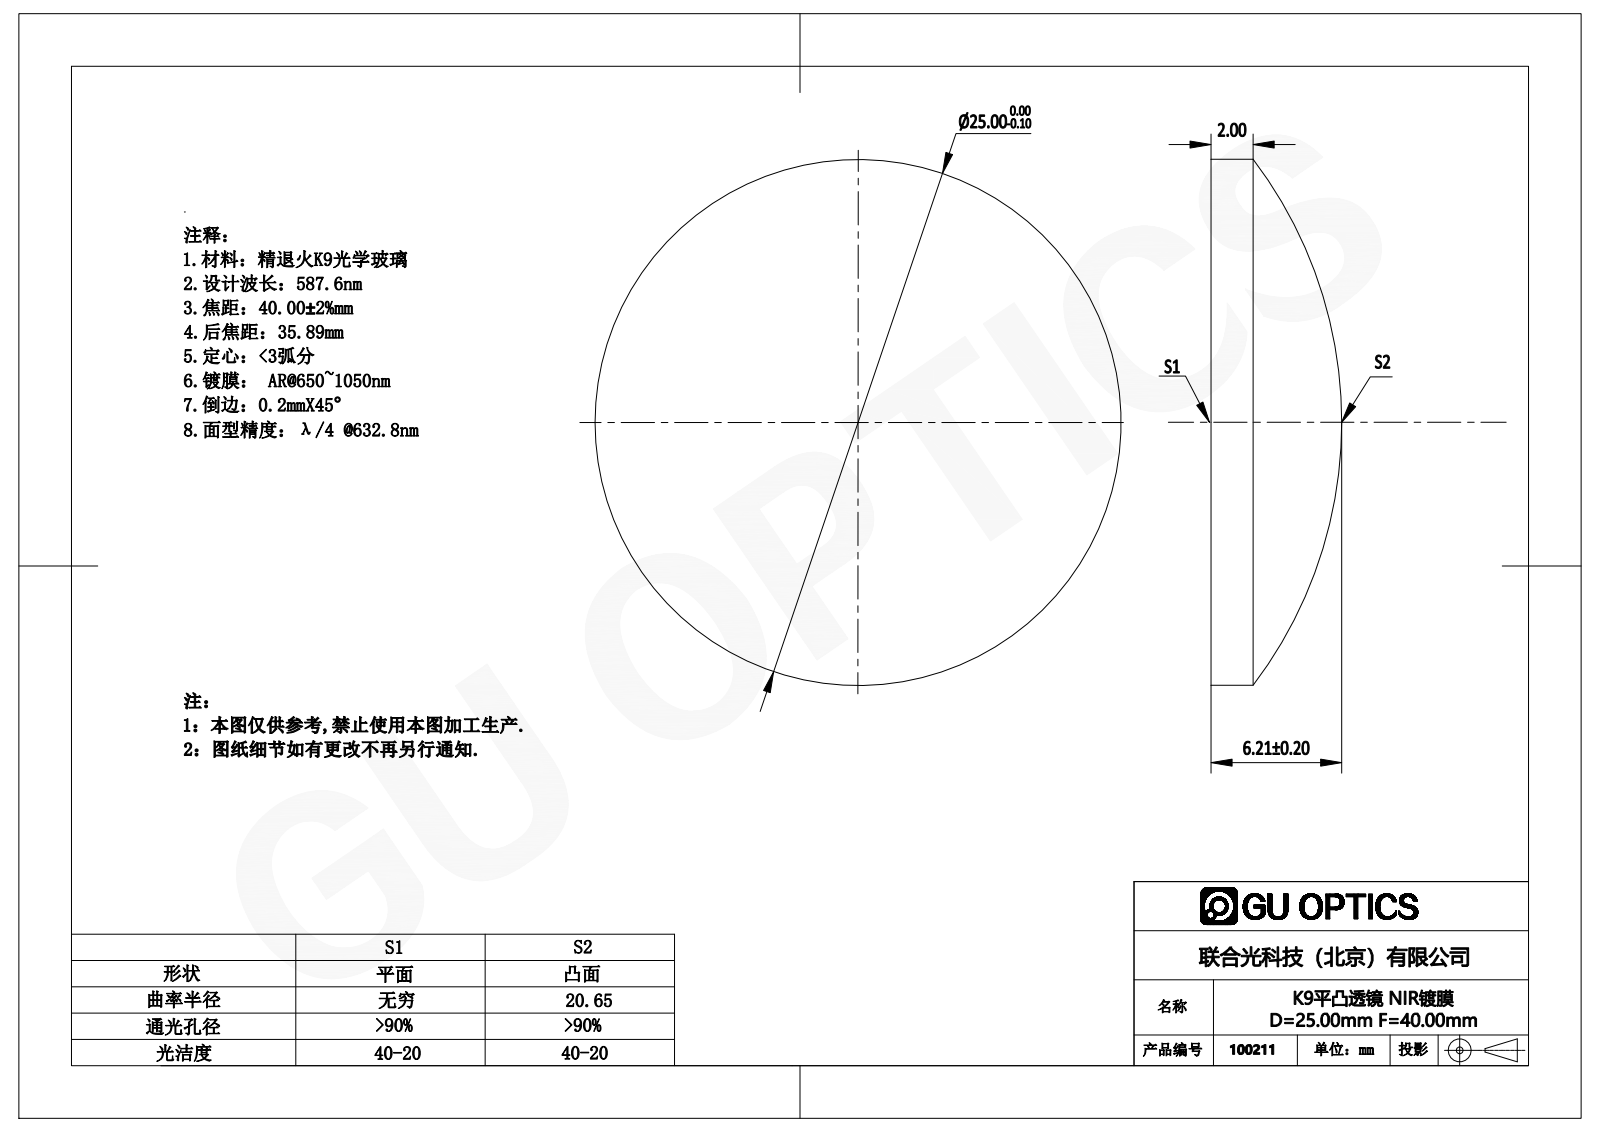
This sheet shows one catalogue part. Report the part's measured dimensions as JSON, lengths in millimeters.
{"part_name": "100211", "step_written_by": "SolidWorks 2016 (AUTOMOTIVE_DESIGN)", "units": "millimeters", "bodies": {"solids": 1, "faces": 5, "planar": 1, "cylindrical": 2, "other": 2}, "overall_size": [25, 25, 6.21], "volume_mm3": 2054, "surface_area_mm2": 1195, "round_bosses_or_shafts": [[25, 1]]}
